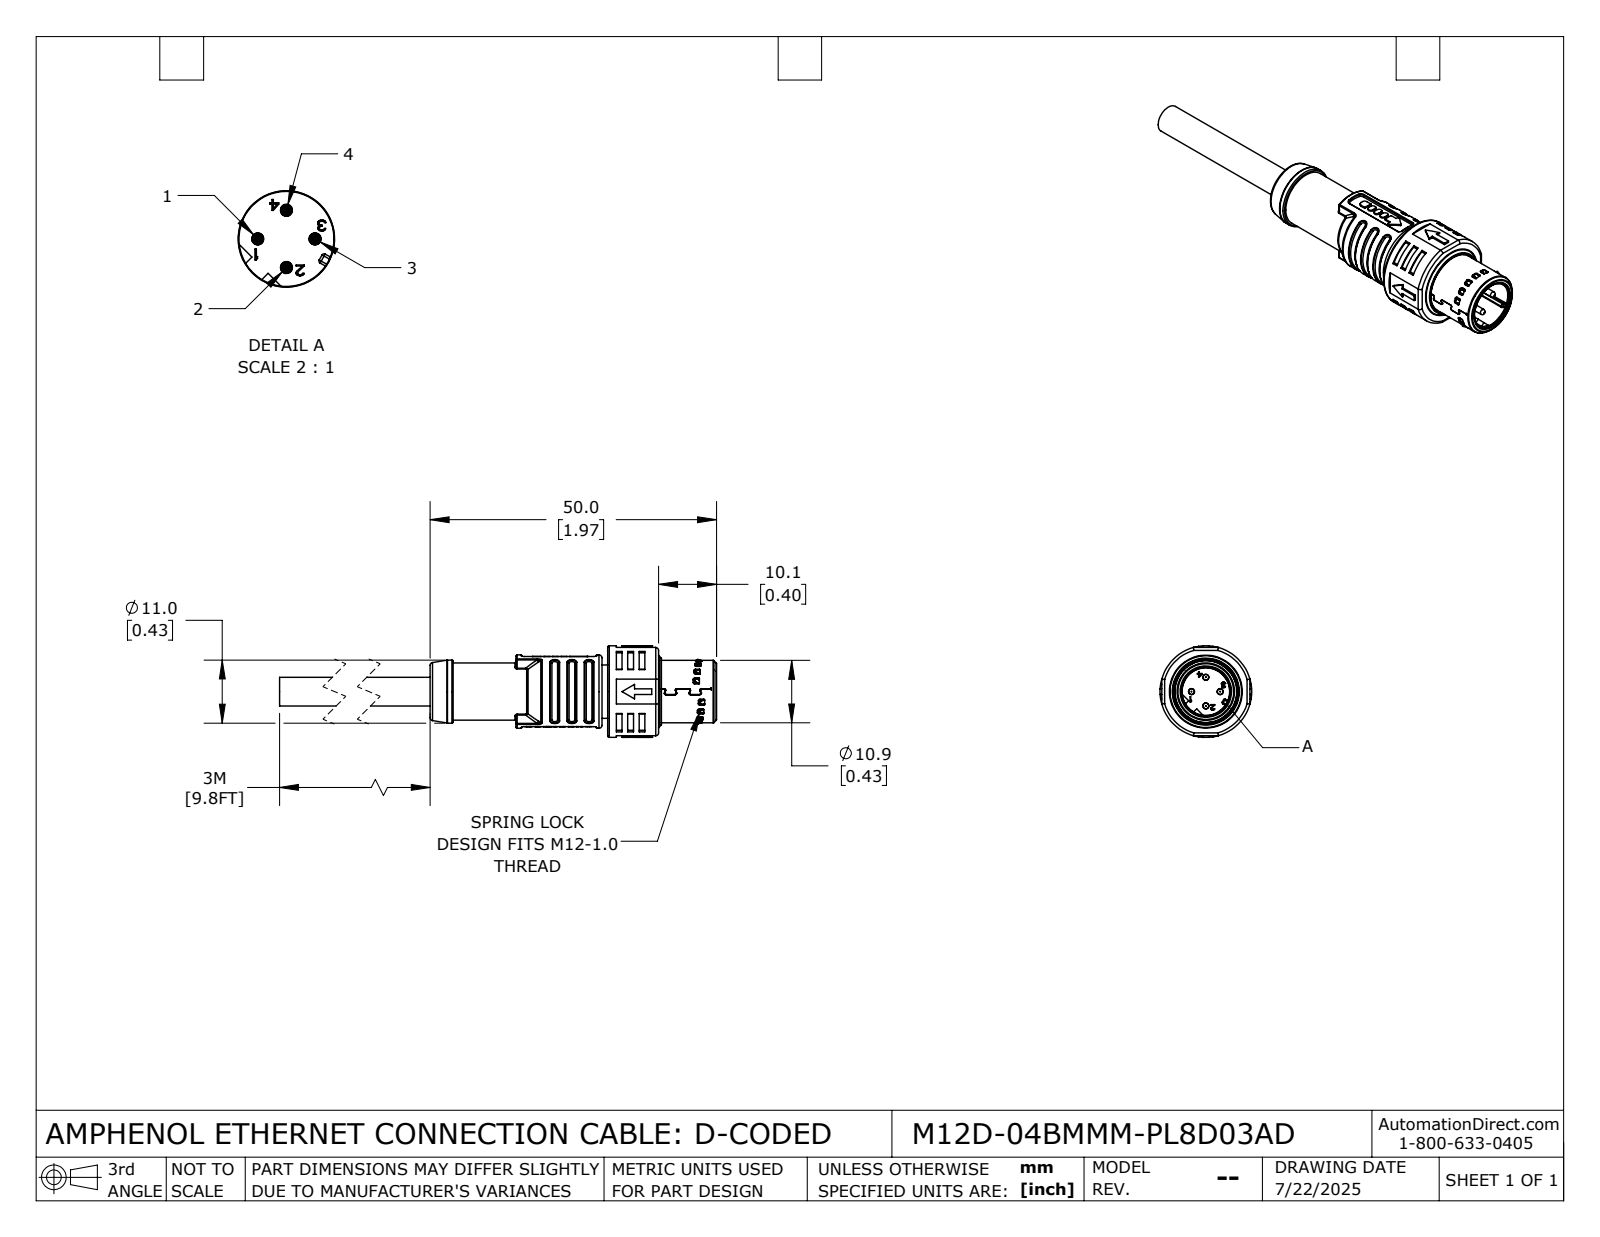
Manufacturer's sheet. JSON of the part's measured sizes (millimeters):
{"part_name": "M12D-04BMMM-PL8D03AD", "step_written_by": "SolidWorks 2024 (CONFIG_CONTROL_DESIGN)", "units": "millimeters", "bodies": {"solids": 1, "faces": 2139, "planar": 996, "cylindrical": 644, "other": 499}, "overall_size": [80, 16, 16], "volume_mm3": 5399, "surface_area_mm2": 5961, "round_holes": [[1.05, 4], [8.3, 1], [9, 1], [10.15, 1], [10.5, 1], [10.9, 1], [11.5, 1], [11.8, 1], [14.2, 1]], "round_bosses_or_shafts": [[1, 4], [16, 1], [14.1, 1], [12.8, 1], [12.4, 1], [11, 1], [10.45, 1], [10.4, 1]], "partial_cylinders_radius": [[0.2, 119], [0.25, 66], [0.3, 64], [0.15, 44], [0.5, 38], [0.13, 12], [0.7, 11], [0.1, 7]], "face_to_face_distances": [1, 30, 10.1, 8.9, 2.5, 1.2, 8.6, 32.5, 15.4, 1.5], "hole_center_spacings": [2.5, 3.54, 5]}
